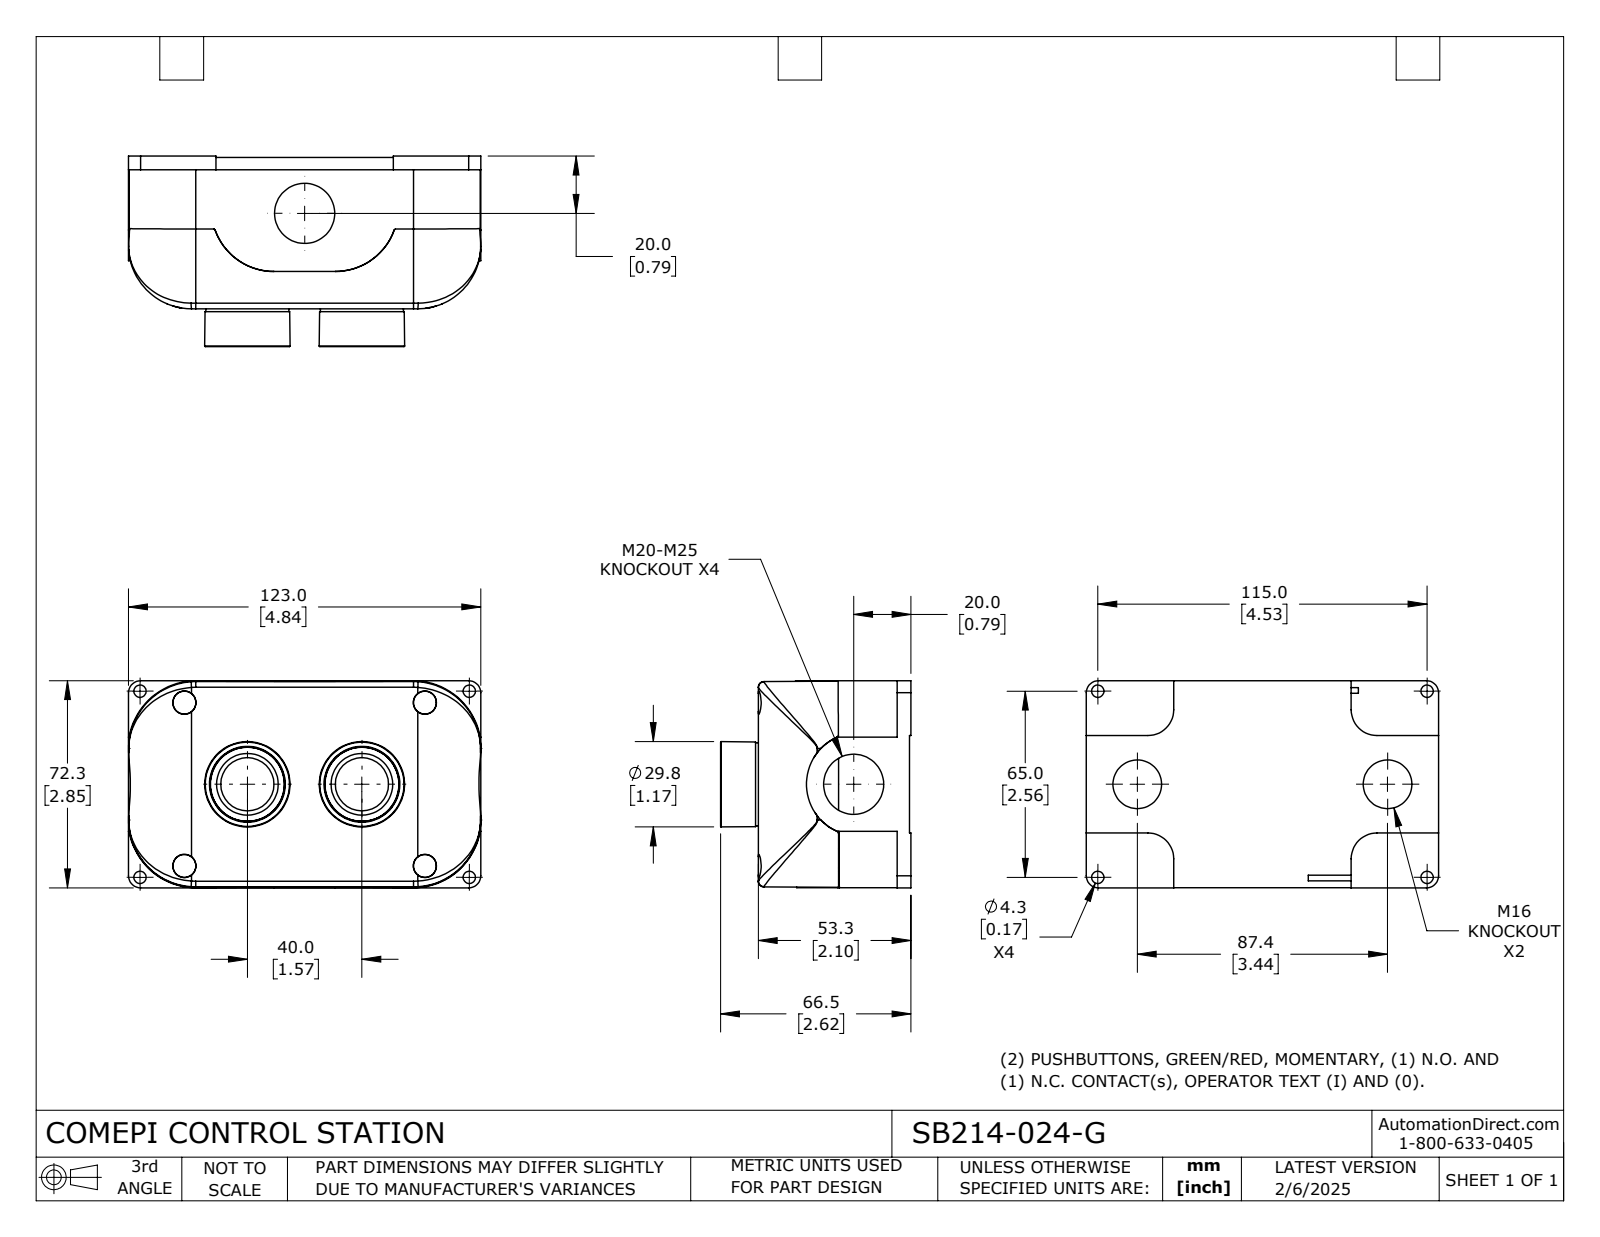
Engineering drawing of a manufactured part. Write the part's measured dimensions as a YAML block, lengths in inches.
part_name: "SB214-024-G"
step_written_by: "SolidWorks 2024 (CONFIG_CONTROL_DESIGN)"
units: inches
bodies: {solids: 8, faces: 427, planar: 185, cylindrical: 106, other: 136}
overall_size: [4.843, 2.846, 2.618]
volume: 16.11
surface_area: 123.7
round_holes:
  - {diameter: 0.169, count: 4}
  - {diameter: 0.531, count: 2}
  - {diameter: 0.669, count: 2}
  - {diameter: 0.827, count: 2}
  - {diameter: 0.854, count: 2}
round_bosses_or_shafts:
  - {diameter: 1.142, count: 2}
  - {diameter: 1.016, count: 2}
  - {diameter: 0.748, count: 2}
  - {diameter: 0.63, count: 2}
  - {diameter: 0.614, count: 2}
partial_cylinders:
  - {radius: 0.01, count: 4}
  - {radius: 0.035, count: 4}
  - {radius: 0.079, count: 4}
  - {radius: 0.157, count: 4}
  - {radius: 0.354, count: 4}
  - {radius: 0.38, count: 4}
  - {radius: 0.866, count: 4}
  - {radius: 0.93, count: 4}
face_to_face_distances: [0.098, 2.079, 1.98, 0.118, 1.102, 0.976, 0.878, 2.098, 0.02, 2.618]
hole_center_spacings: [1.39, 1.954, 3.309, 4.185, 0.933, 2.508, 2.559, 4.528]
